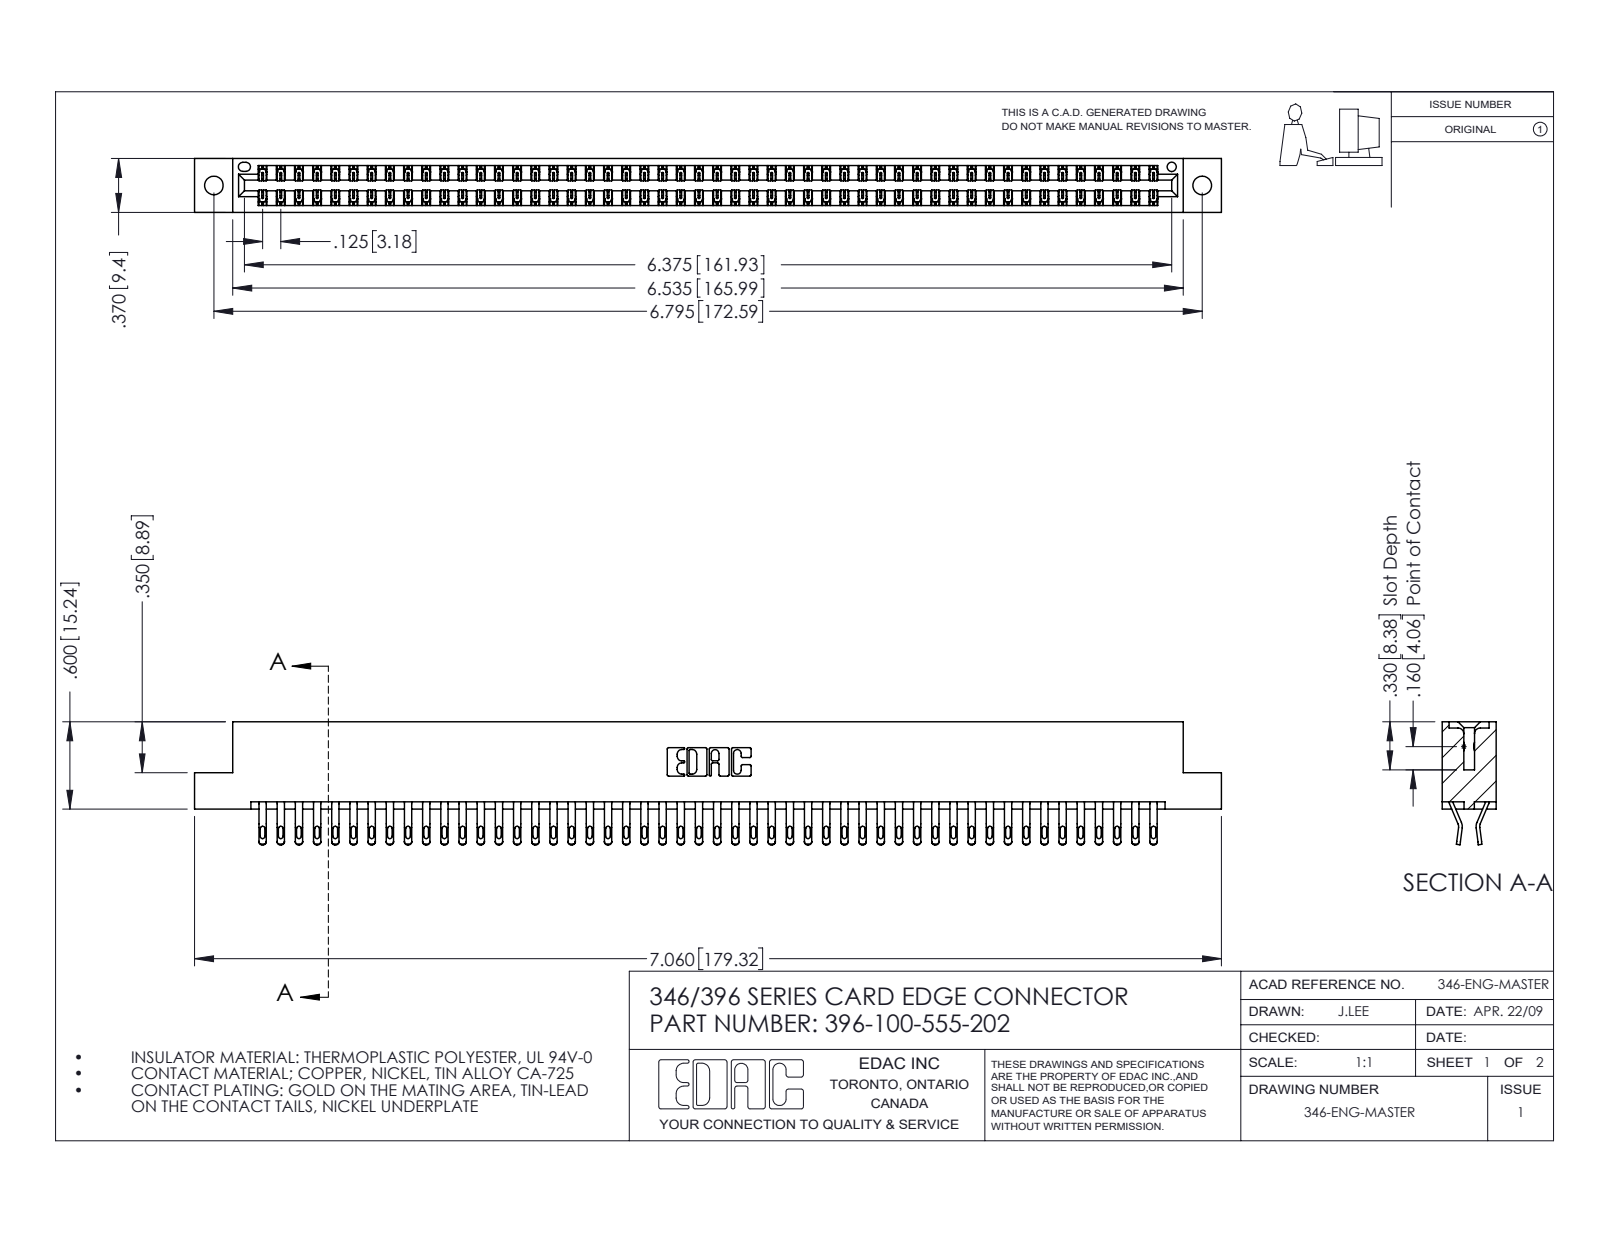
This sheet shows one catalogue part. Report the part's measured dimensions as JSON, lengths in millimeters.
{"part_name": "396-100-555-202; 346 Part_Flush Mounting Lugs - 0.128 Dia; 345-292-001_555 Tail", "step_written_by": "SolidWorks 2016 (CONFIG_CONTROL_DESIGN)", "units": "millimeters", "bodies": {"solids": 101, "faces": 5922, "planar": 3376, "cylindrical": 2546, "other": 0}, "overall_size": [179.3, 21.5, 9.4], "volume_mm3": 17800, "surface_area_mm2": 25360, "round_holes": [[3.3, 2], [1.6, 1]], "partial_cylinders_radius": [[0.4, 200], [0.5, 200], [0.2, 150], [0.3, 22], [0.2, 6], [0.8, 6], [0.7, 3], [0.3, 2]], "face_to_face_distances": [1.2, 8.2, 9.4, 6.4, 0.6, 1.8, 7.6, 7, 3.8, 5.6], "hole_center_spacings": [6.2, 167.3, 172.6]}
